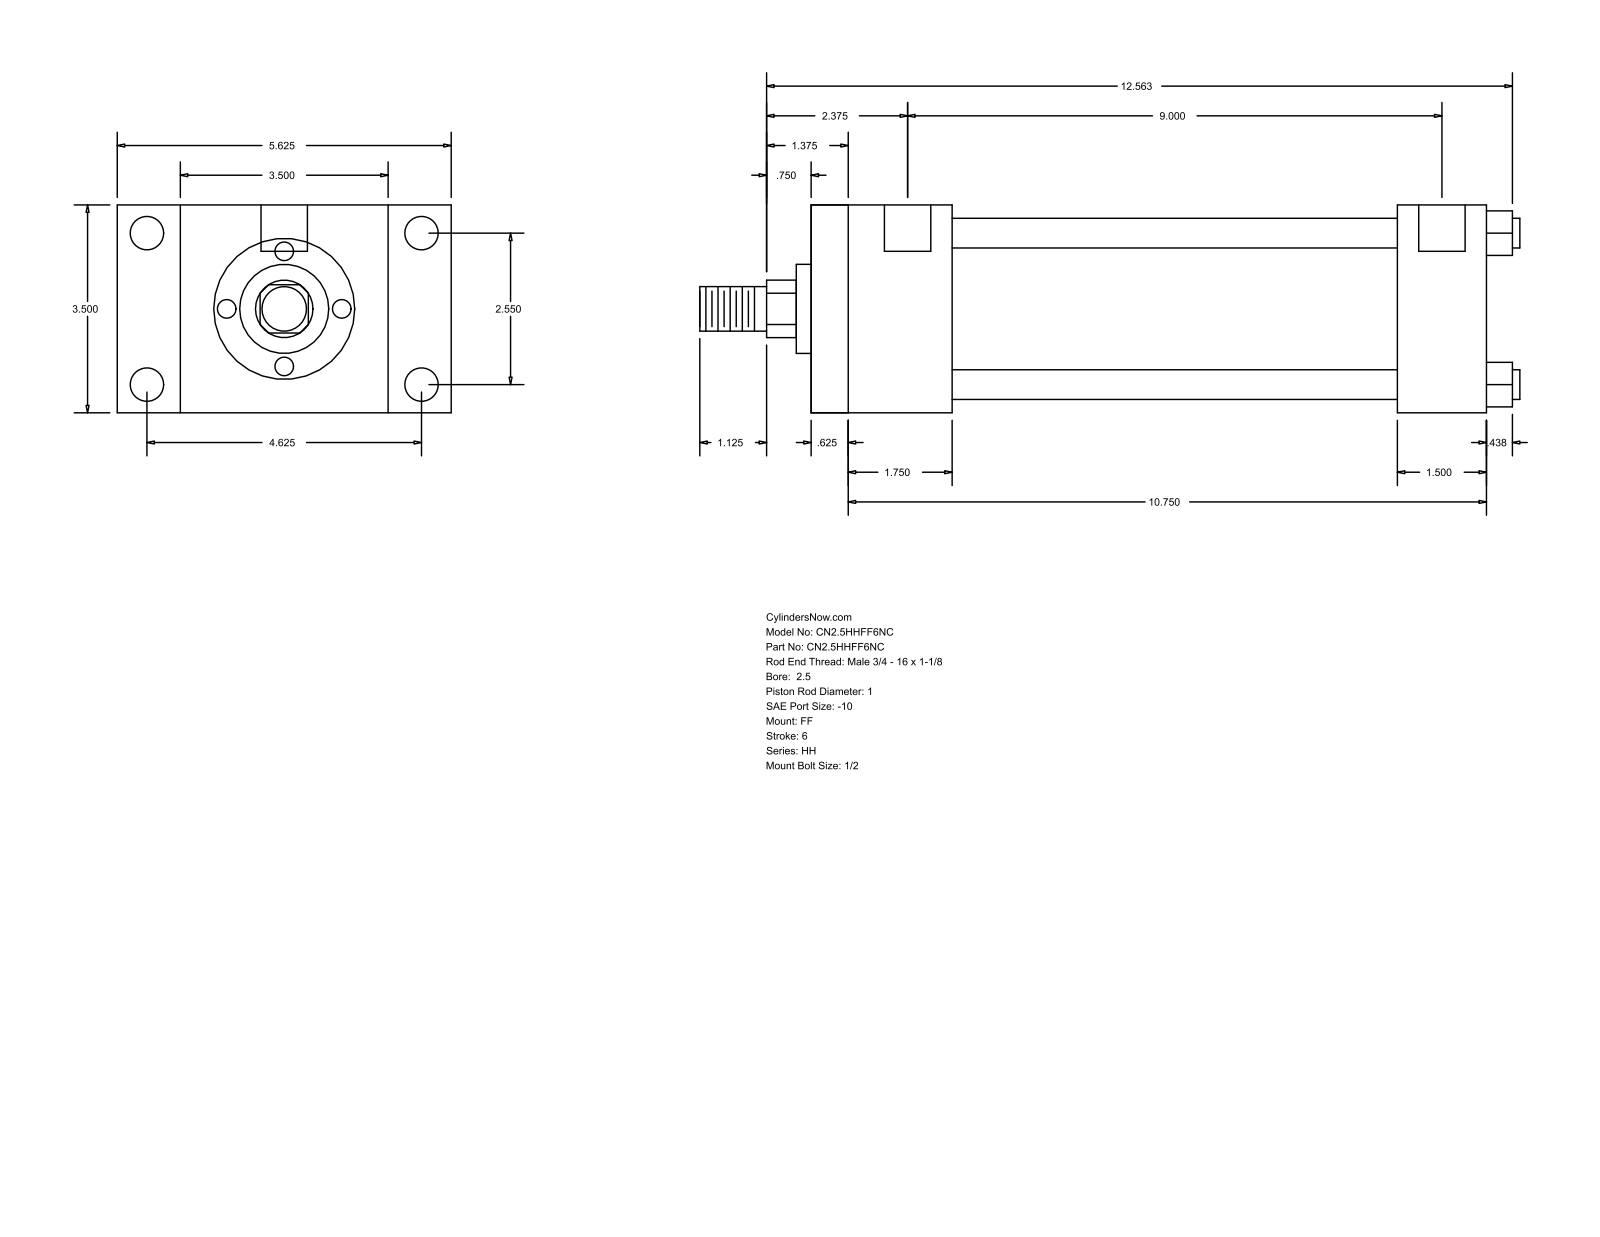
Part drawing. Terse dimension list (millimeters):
name: HH_FF__0250_1
written by: GSSL Pune (CONFIG_CONTROL_DESIGN)
unit: mm
bodies: 0 solids, 92 faces (64 planar, 28 cylindrical, 0 other)
size: 350.84 × 142.88 × 88.9
holes: 4× ⌀5.56, 4× ⌀14.3, 2× ⌀19.84
bosses: 4× ⌀12.7, 1× ⌀73.03, 1× ⌀38.1, 1× ⌀25.4, 1× ⌀19.05
rounds: 1× R12.29
face distances: 88.9, 288.93, 15.87, 273.06, 38.1, 60.33, 44.46, 228.6, 250.83, 234.96
hole spacings: 64.76, 117.48, 134.15, 231.77, 1.58, 1.59, 228.6, 230.18
